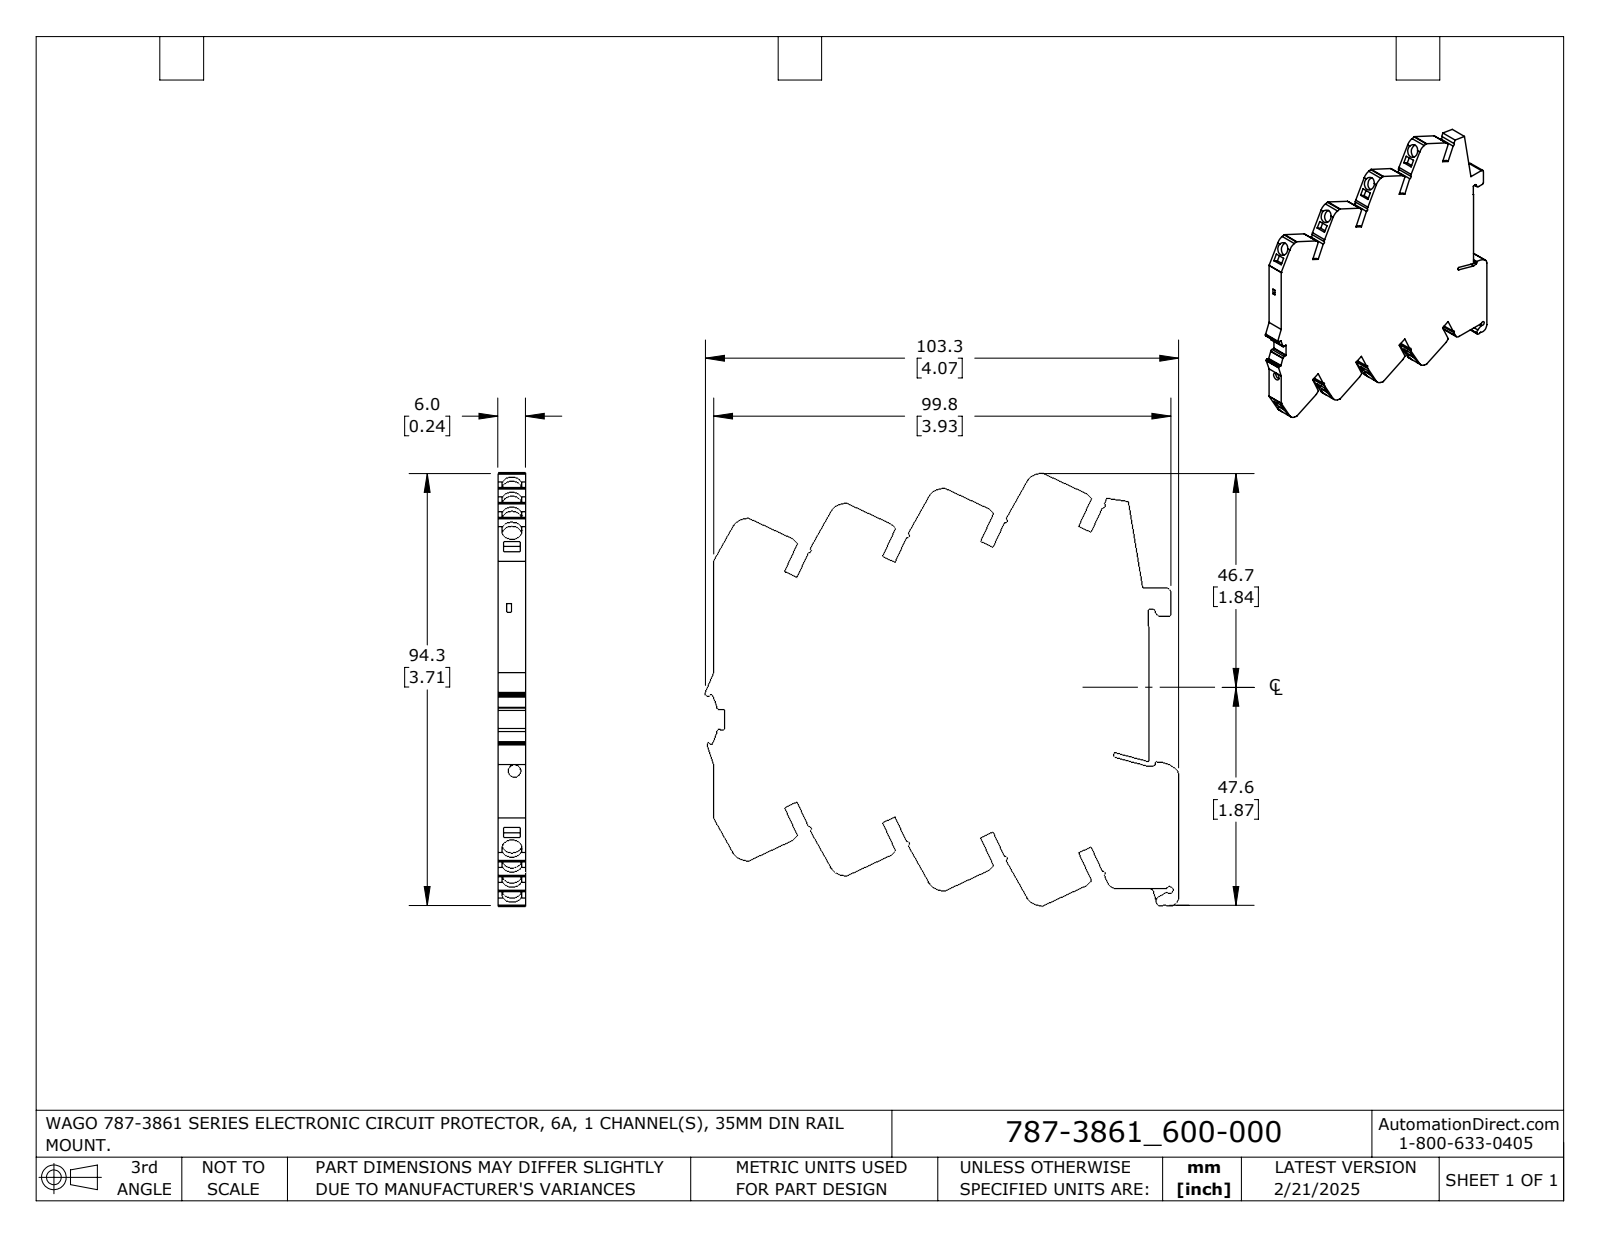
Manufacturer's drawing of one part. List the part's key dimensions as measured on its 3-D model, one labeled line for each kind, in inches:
Part name (STEP PRODUCT): 787-3861_600-000_HI
STEP written by: SolidWorks 2024 (AUTOMOTIVE_DESIGN)
Units: inches
Bodies: 1 solid, 262 faces (197 planar, 65 cylindrical, 0 other)
Overall size (bounding box): 4.067 × 3.711 × 0.236
Volume: 2.685 in³ · Surface area: 29.24 in²
Round holes (diameter × count): ⌀0.173 ×8, ⌀0.106 ×1
Partial cylindrical surfaces — rounded edges, fillets, slot ends (radius × count): R0.008 ×13, R0.02 ×12, R0.016 ×8, R0.132 ×8, R0.039 ×5, R0.012 ×3, R0.079 ×3, R0.018 ×2
Main face-to-face distances: 0.236, 0.708, 0.67, 0.473, 0.118, 1.417, 0.472, 0.945, 0.59, 1.34
Hole centre spacings: 0.526, 0.525, 1.051, 1.052, 1.577
